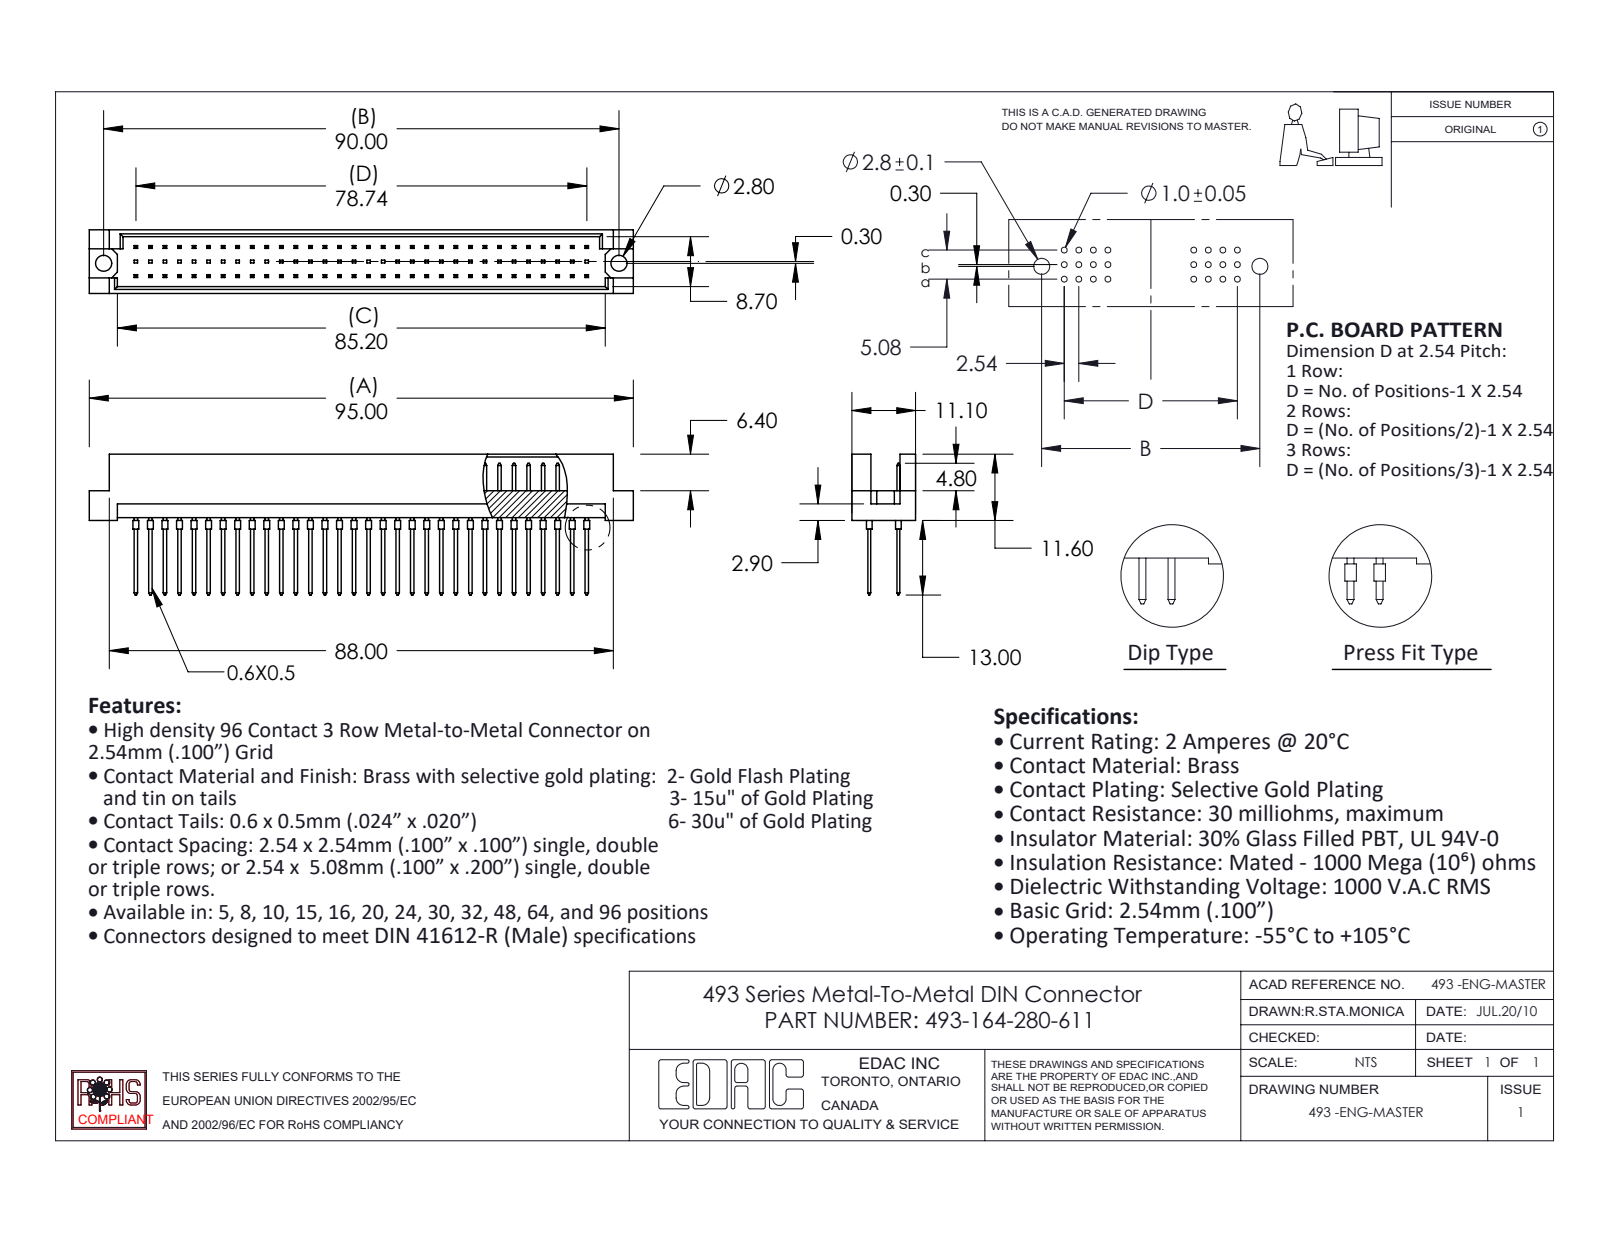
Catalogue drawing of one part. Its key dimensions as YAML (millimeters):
part_name: "493-164-280-611; 493 Part_96; 493-290_80"
step_written_by: "SolidWorks 2020 (CONFIG_CONTROL_DESIGN)"
units: millimeters
bodies: {solids: 65, faces: 1844, planar: 1712, cylindrical: 132, other: 0}
overall_size: [95, 24.6, 11.1]
volume: 6140
surface_area: 9840
round_holes:
  - {diameter: 2.8, count: 2}
round_bosses_or_shafts:
  - {diameter: 1, count: 64}
face_to_face_distances: [1.2, 9.9, 5.08, 0.5, 2.76, 3.26, 7.84, 8.34, 1.56, 2.06]
hole_center_spacings: [90]
